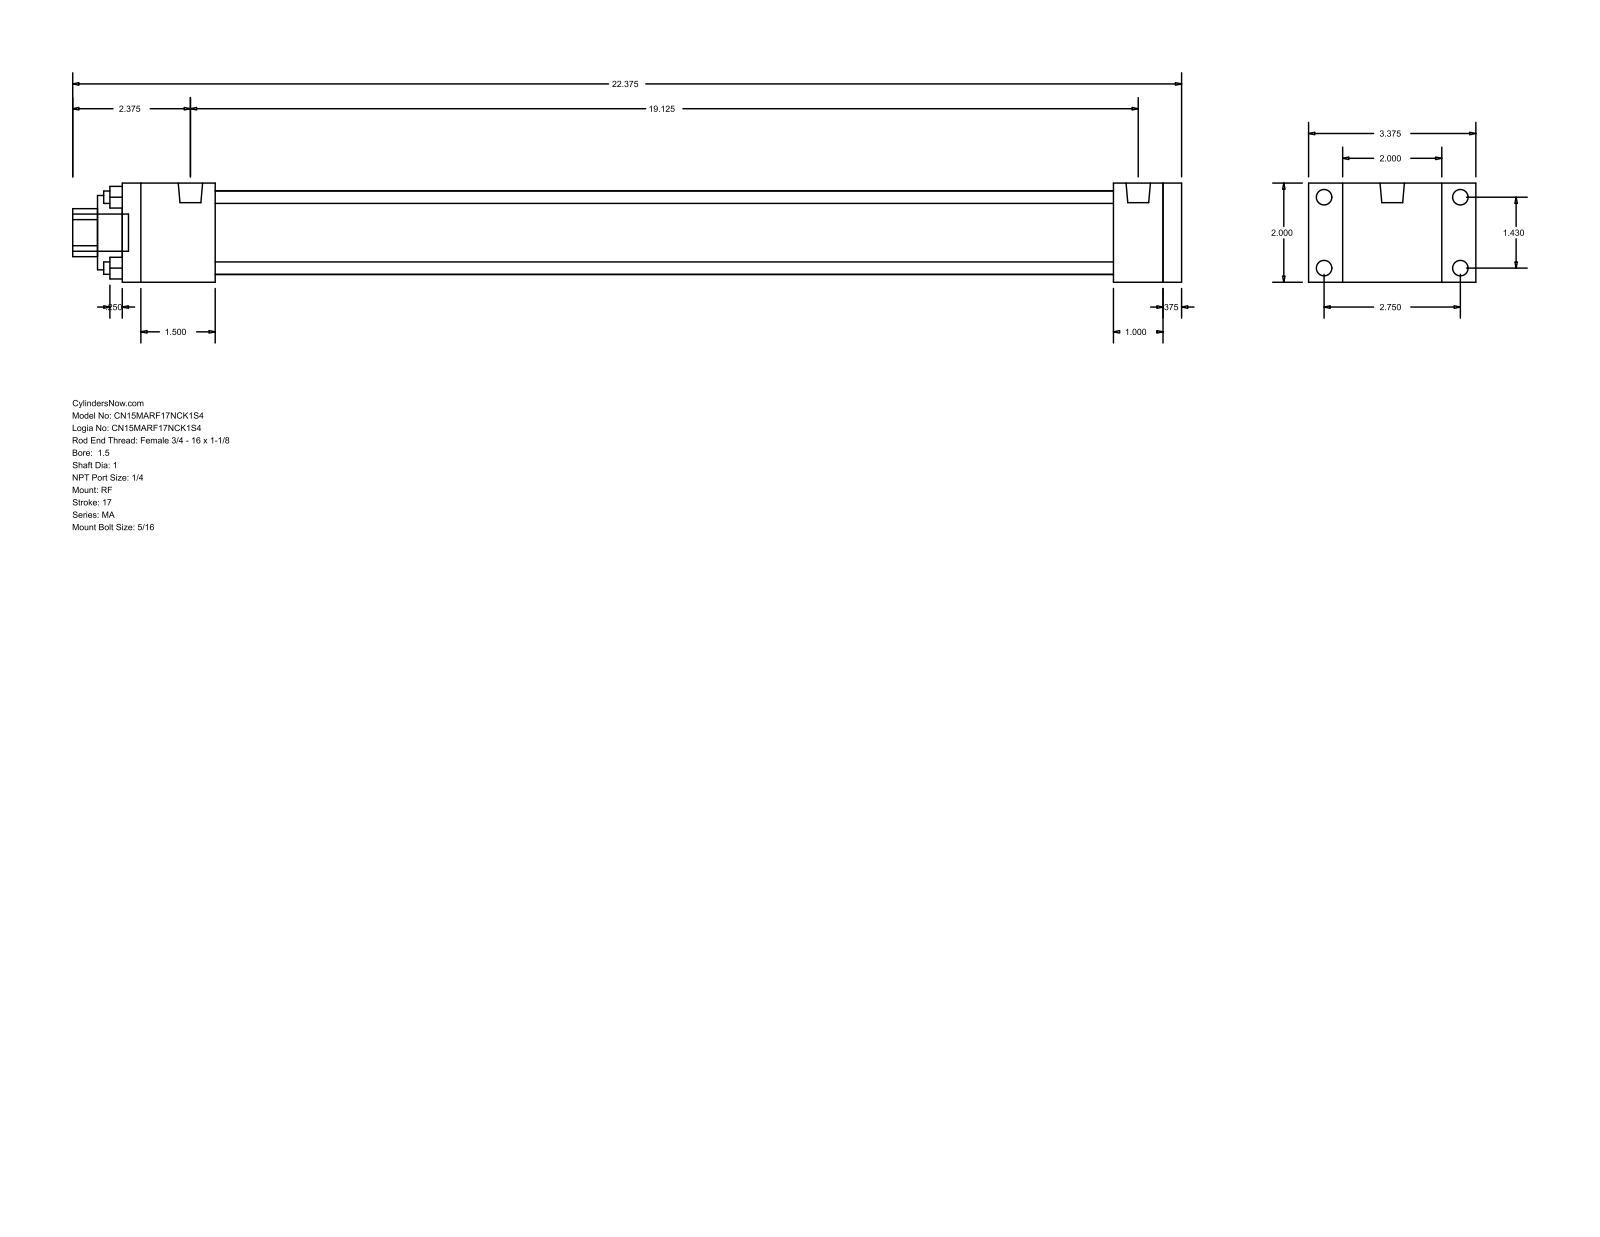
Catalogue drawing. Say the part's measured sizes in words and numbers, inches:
The part is named "MA_RF__0150_1". Its 3-D file was written by "GSSL Pune (CONFIG_CONTROL_DESIGN)". It is 0 solids with 92 faces: 64 planar, 28 cylindrical and 0 other. Overall it measures 22.375 by 3.375 by 2 inches. Round holes: 4 of diameter 0.25, 1 of diameter 1, 1 of diameter 1.5, 1 of diameter 1.69. Round bosses or shafts: 8 of diameter 0.313, 2 of diameter 0.492, 1 of diameter 0.75. Partial cylindrical surfaces (rounded edges, fillets, slot ends): 1 of radius 0.484. The main face-to-face distances are 2, 0.375, 21, 1, 21.375, 20, 1.375, 1.875, 18.125, 19.125. The hole center spacings are 1.011, 1.43, 2.022.
